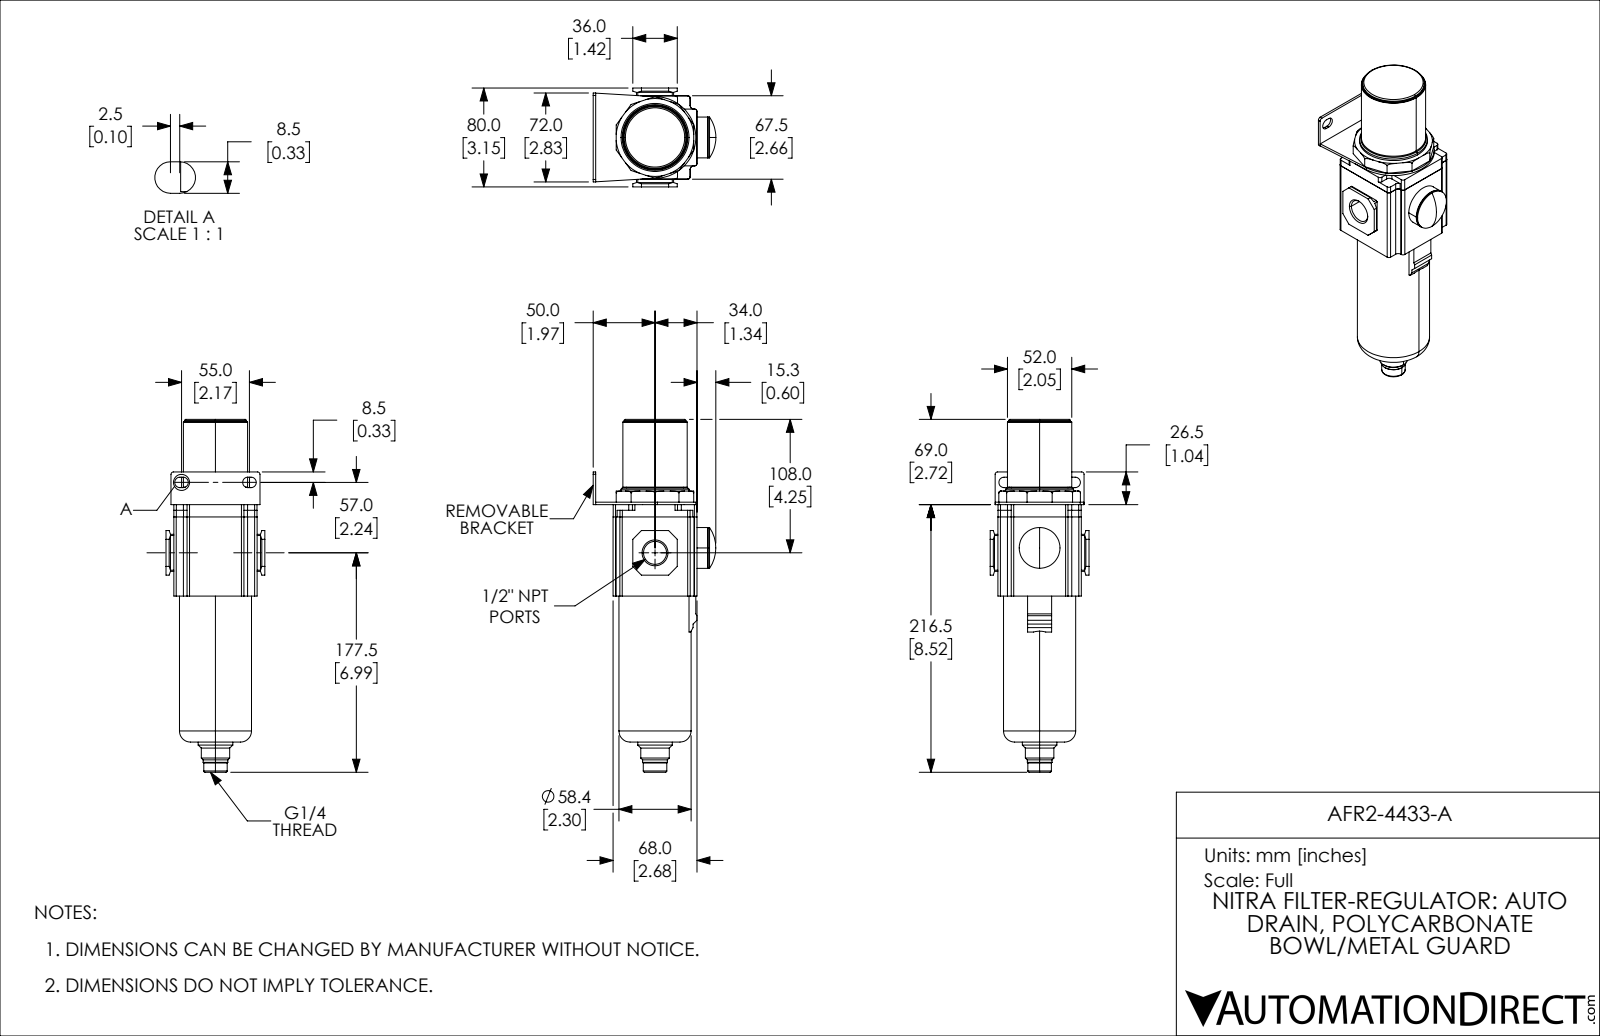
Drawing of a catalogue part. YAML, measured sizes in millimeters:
part_name: "AFR2-4433-A"
step_written_by: "SolidWorks 2019 (CONFIG_CONTROL_DESIGN)"
units: millimeters
bodies: {solids: 1, faces: 222, planar: 119, cylindrical: 67, other: 36}
overall_size: [285.5, 99.28, 80]
volume: 822072
surface_area: 76004
round_holes:
  - {diameter: 11.45, count: 1}
  - {diameter: 18.63, count: 1}
round_bosses_or_shafts:
  - {diameter: 58.4, count: 1}
  - {diameter: 55, count: 1}
  - {diameter: 52, count: 1}
  - {diameter: 50, count: 1}
  - {diameter: 45.9, count: 1}
  - {diameter: 33, count: 1}
  - {diameter: 28, count: 1}
  - {diameter: 23, count: 1}
partial_cylinders:
  - {radius: 2, count: 22}
  - {radius: 3, count: 12}
  - {radius: 4.25, count: 4}
  - {radius: 33, count: 1}
face_to_face_distances: [2, 67.5, 67, 68, 16, 69, 84, 6.25, 73.75, 76]
